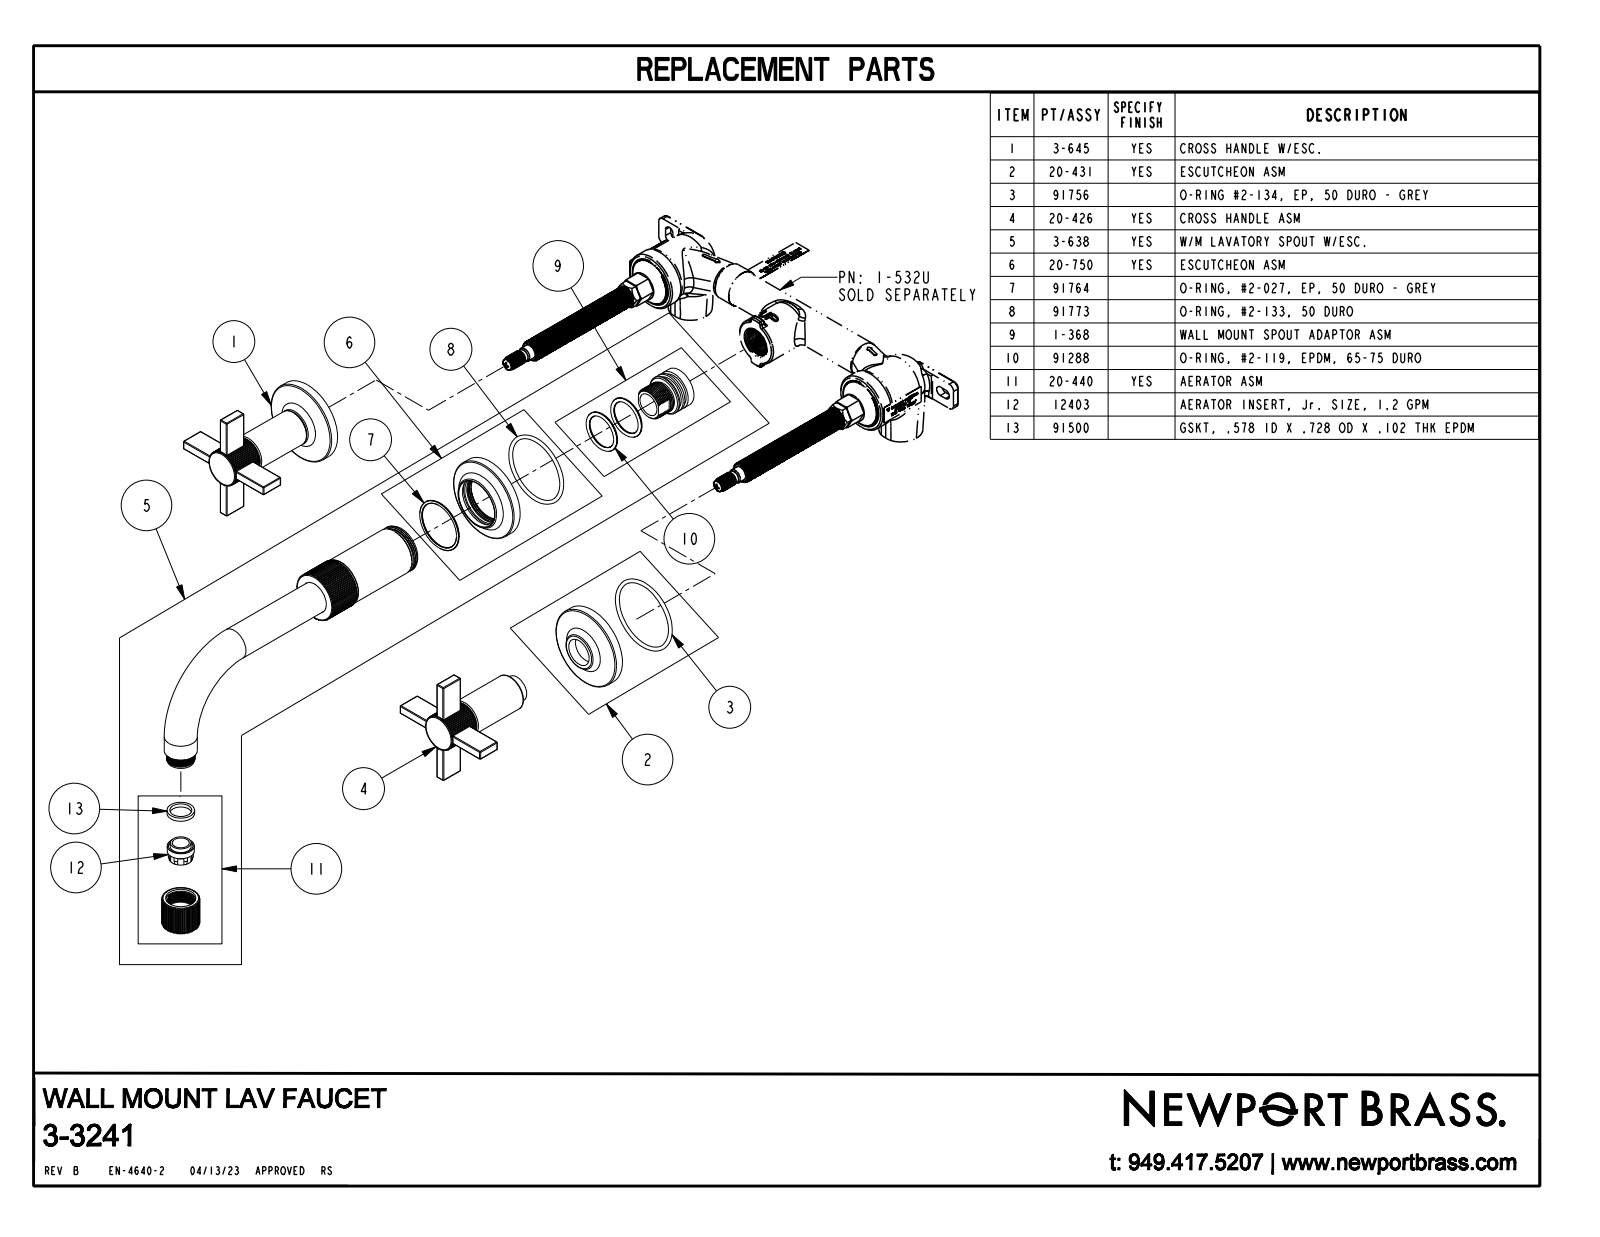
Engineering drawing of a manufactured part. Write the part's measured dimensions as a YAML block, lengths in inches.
part_name: "3-3241_SW0001"
step_written_by: "CREO PARAMETRIC BY PTC INC, 2018400 (AUTOMOTIVE_DESIGN)"
units: inches
bodies: {solids: 3, faces: 1291, planar: 731, cylindrical: 462, other: 98}
overall_size: [10.874, 8.75, 4.76]
volume: 18
surface_area: 100.5
round_bosses_or_shafts:
  - {diameter: 2.25, count: 3}
  - {diameter: 1, count: 2}
  - {diameter: 0.875, count: 2}
  - {diameter: 0.85, count: 2}
  - {diameter: 0.52, count: 2}
  - {diameter: 1.312, count: 1}
  - {diameter: 1.28, count: 1}
partial_cylinders:
  - {radius: 0.02, count: 40}
  - {radius: 0.03, count: 12}
  - {radius: 0.47, count: 2}
  - {radius: 0.5, count: 1}
  - {radius: 0.675, count: 1}
face_to_face_distances: [7.874, 0.25, 0.25, 0.624, 3.146, 2.496, 0.65, 3.201, 0.705, 0.055]
